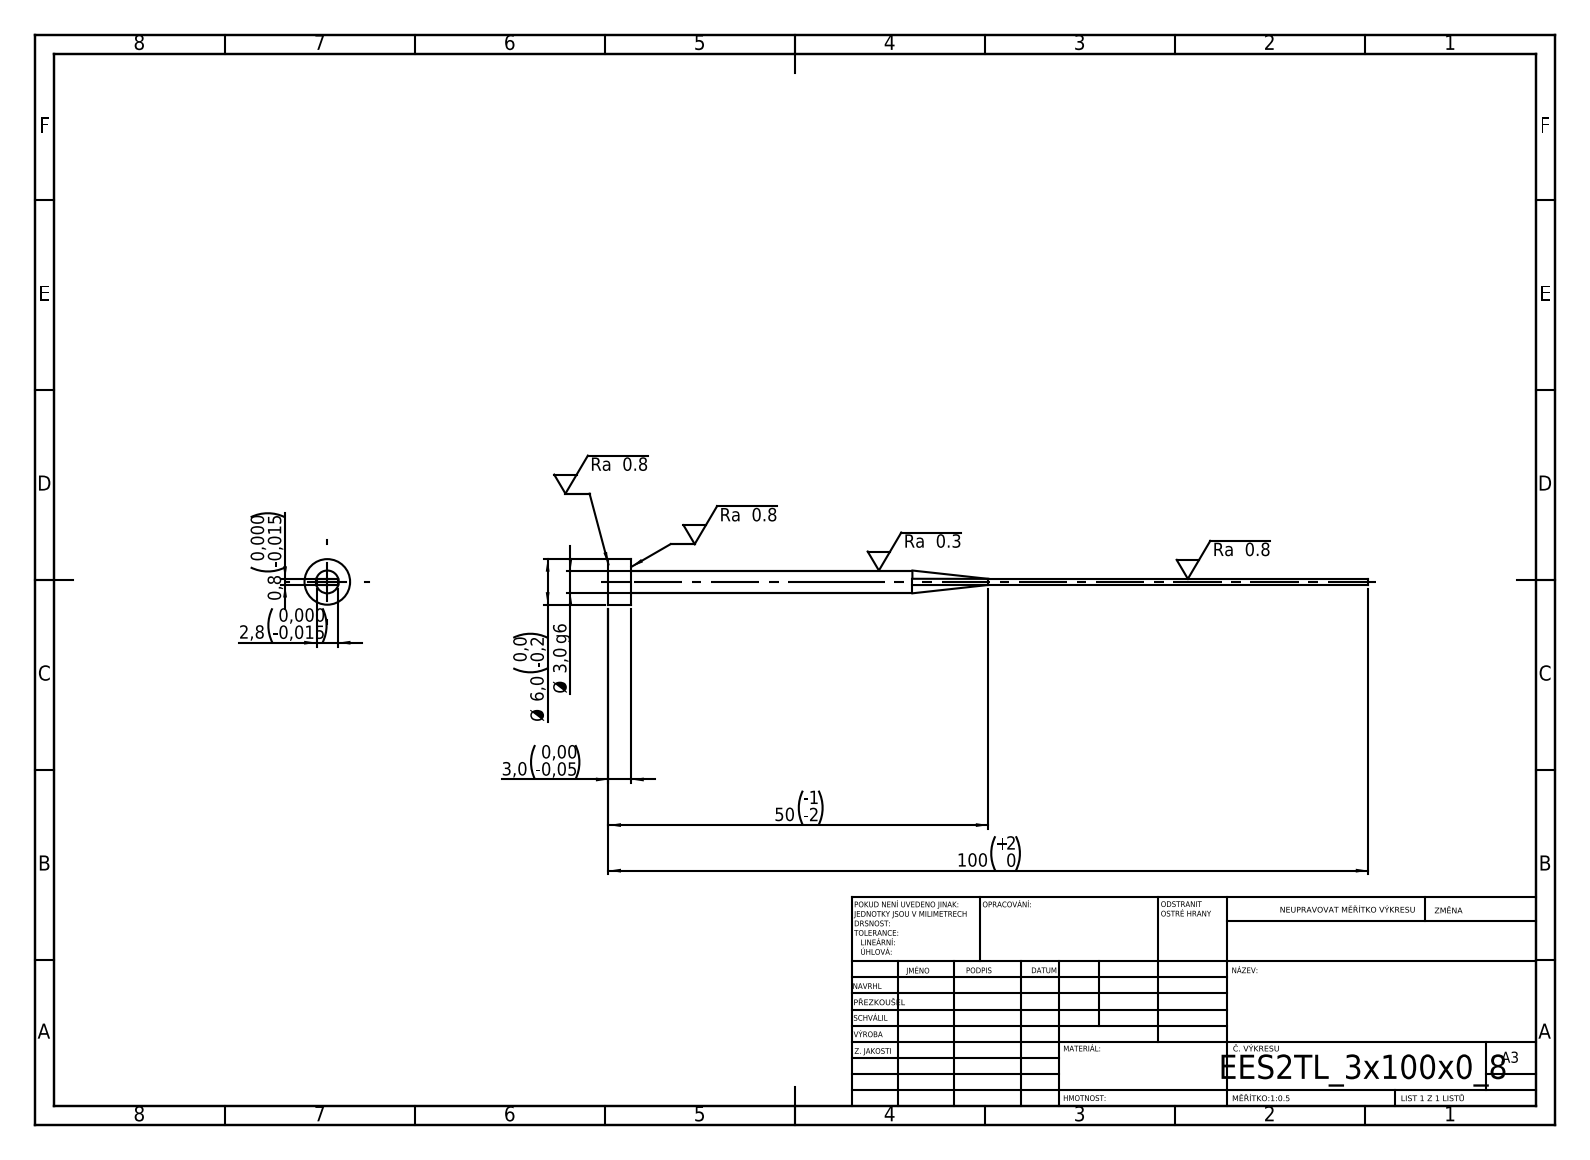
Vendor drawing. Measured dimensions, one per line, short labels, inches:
written by: SolidWorks 2019 (CONFIG_CONTROL_DESIGN)
unit: in
bodies: 1 solid, 15 faces (7 planar, 4 cylindrical, 4 other)
size: 3.937 × 0.236 × 0.236
volume: 0.031 in³; area: 1.39 in²
bosses: 1× ⌀0.236, 1× ⌀0.118
face distances: 0.031, 0.11, 0.118, 3.937, 3.819
